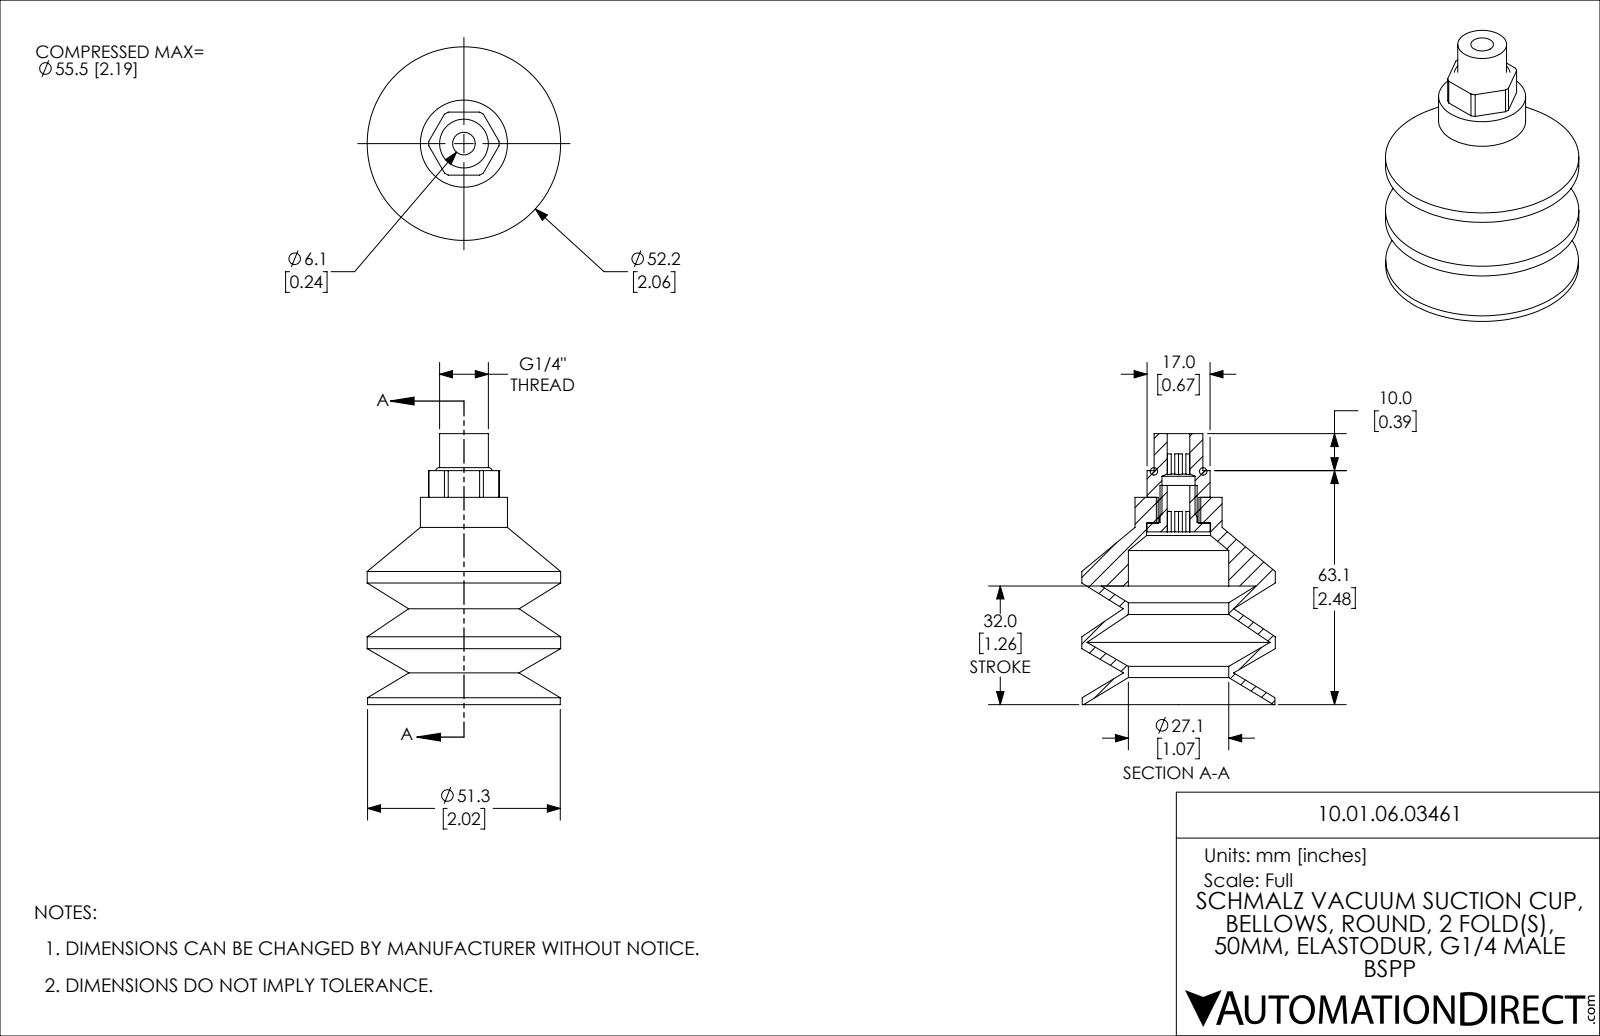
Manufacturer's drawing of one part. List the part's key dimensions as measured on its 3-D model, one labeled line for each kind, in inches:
Part name (STEP PRODUCT): 10.01.06.03461
STEP written by: SolidWorks 2021 (CONFIG_CONTROL_DESIGN)
Units: inches
Bodies: 4 solids, 122 faces (53 planar, 41 cylindrical, 28 other)
Overall size (bounding box): 2.878 × 2.055 × 2.055
Volume: 2.093 in³ · Surface area: 36.8 in²
Round holes (diameter × count): ⌀0.24 ×1, ⌀0.351 ×1, ⌀0.402 ×1, ⌀0.433 ×1, ⌀0.681 ×1, ⌀1.067 ×1
Round bosses / shafts (diameter × count): ⌀2.055 ×1, ⌀2.047 ×1, ⌀0.925 ×1, ⌀0.669 ×1, ⌀0.518 ×1, ⌀0.472 ×1, ⌀0.394 ×1
Partial cylindrical surfaces — rounded edges, fillets, slot ends (radius × count): R0.374 ×1
Main face-to-face distances: 0.941, 0.575, 0.366, 0.669, 0.673, 0.098, 0.268, 0.551, 0.217, 0.394
